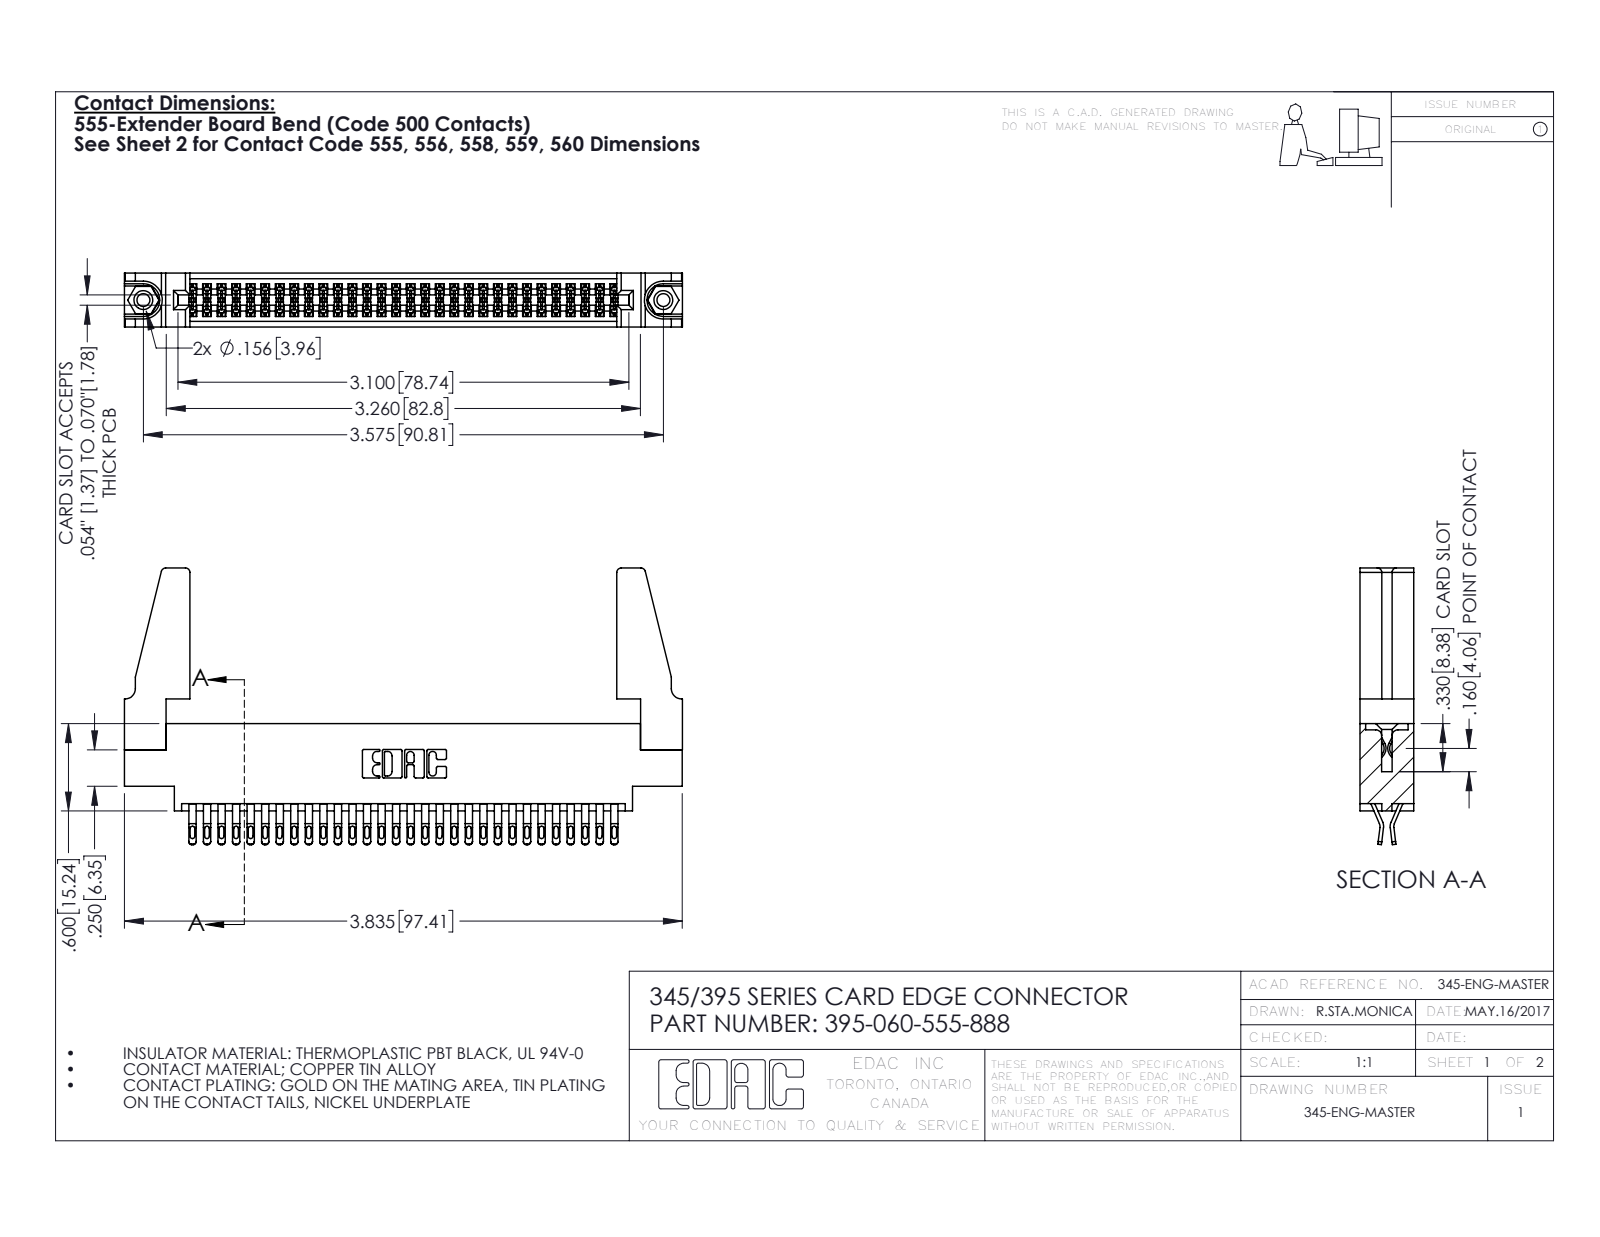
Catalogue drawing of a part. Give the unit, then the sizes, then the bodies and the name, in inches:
Units: inches
Overall size (bounding box): 3.836 × 1.902 × 0.37
Round holes (diameter × count): ⌀0.089 ×2, ⌀0.125 ×2, ⌀0.156 ×2, ⌀0.064 ×1
Round bosses / shafts (diameter × count): ⌀0.155 ×2
Partial cylindrical surfaces — rounded edges, fillets, slot ends (radius × count): R0.016 ×150, R0.02 ×120, R0.006 ×90, R0.01 ×22, R0.03 ×8, R0.007 ×6, R0.031 ×6, R0.026 ×3
Main face-to-face distances: 0.072, 0.37, 0.298, 0.025, 0.2, 0.098, 0.272, 0.225, 0.175, 0.149
Hole centre spacings: 0.27, 3.34, 3.575
Volume: 0.773 in³ · Surface area: 27.21 in²
Bodies: 65 solids, 3614 faces (2016 planar, 1582 cylindrical, 16 other)
Part name (STEP PRODUCT): 345 Part_0.170 Offset - 0.156 Dia-TH; 345-250-001_345-250-001-102; 395-060-555-888; 345-292-001_555 Tail (+1 more)
STEP written by: SolidWorks 2016 (CONFIG_CONTROL_DESIGN)
